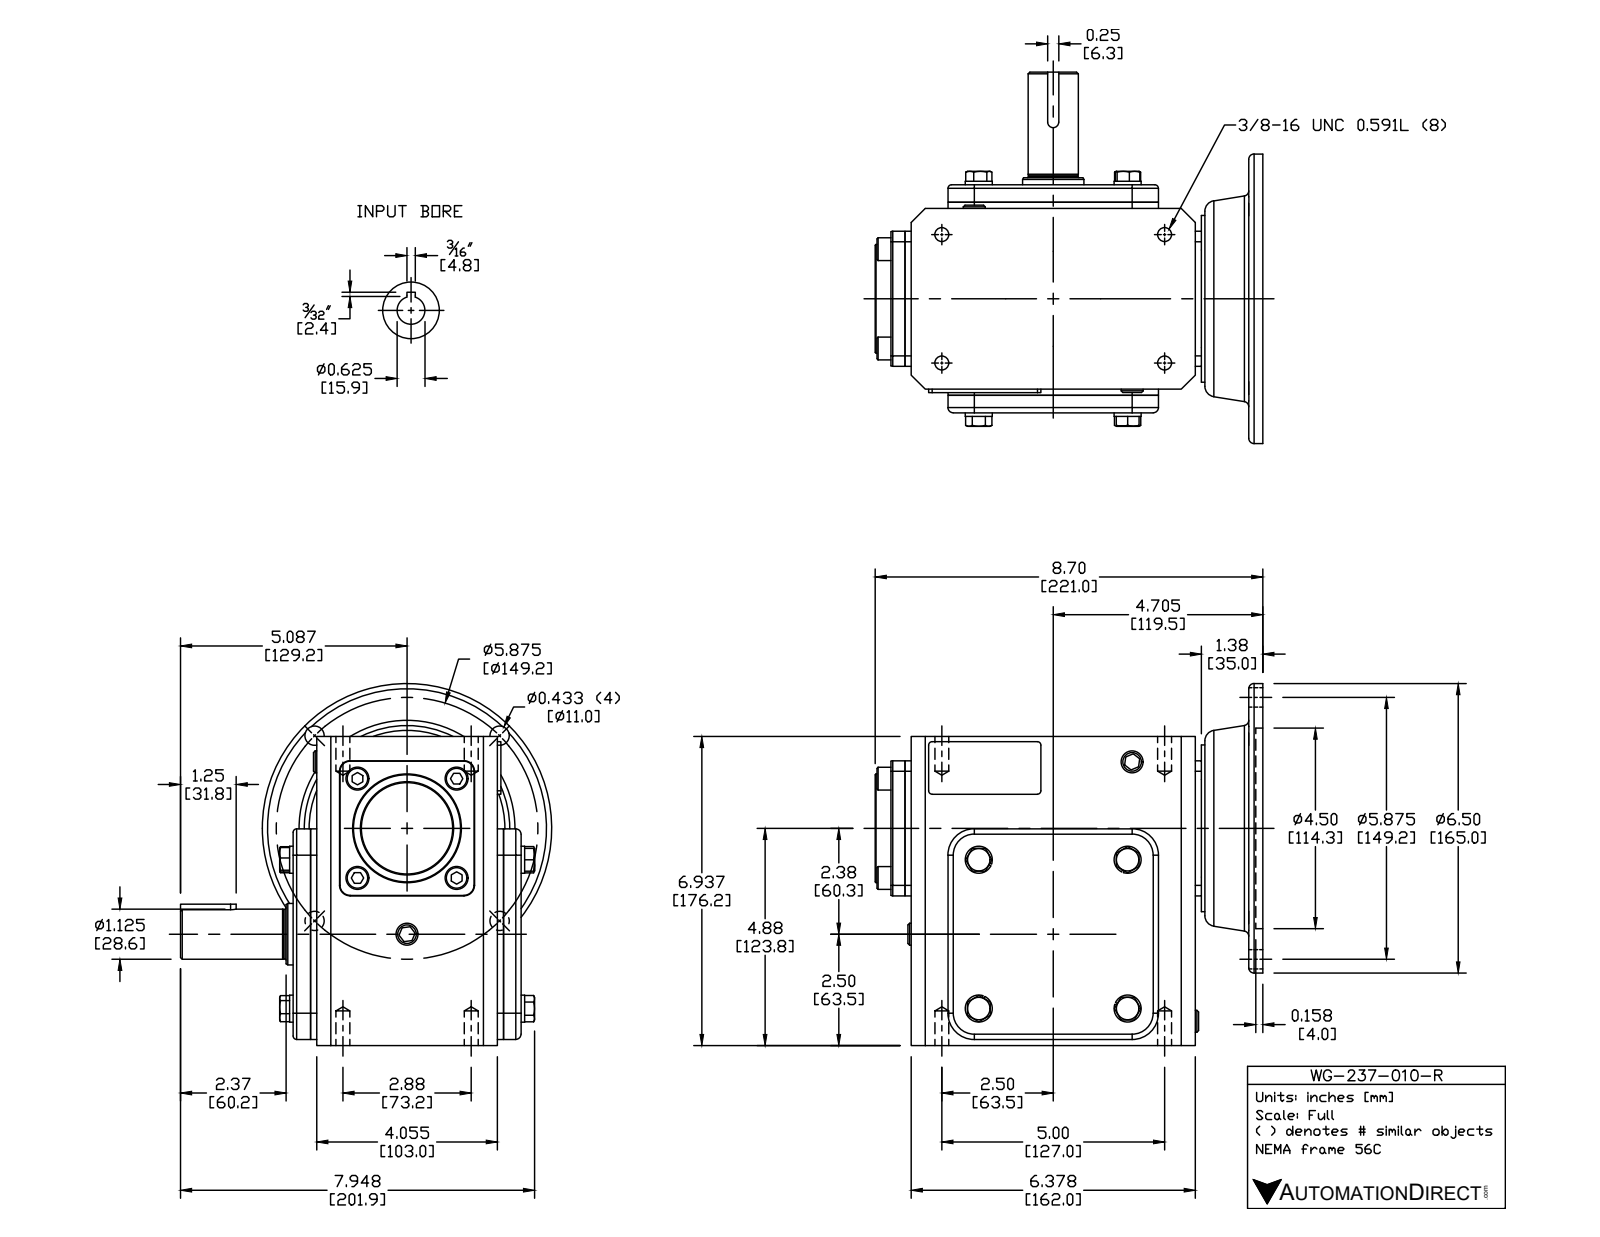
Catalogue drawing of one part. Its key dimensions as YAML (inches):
part_name: "WG-237-010-R"
step_written_by: "SolidWorks 2015 (CONFIG_CONTROL_DESIGN)"
units: inches
bodies: {solids: 37, faces: 537, planar: 294, cylindrical: 153, other: 90}
overall_size: [8.701, 8.335, 8.123]
volume: 222.4
surface_area: 508.3
round_holes:
  - {diameter: 0.313, count: 4}
  - {diameter: 0.406, count: 4}
  - {diameter: 0.591, count: 1}
  - {diameter: 0.625, count: 1}
  - {diameter: 1.378, count: 1}
  - {diameter: 1.457, count: 1}
  - {diameter: 1.772, count: 1}
  - {diameter: 3.819, count: 1}
  - {diameter: 4.5, count: 1}
round_bosses_or_shafts:
  - {diameter: 0.606, count: 4}
  - {diameter: 0.512, count: 4}
  - {diameter: 6.496, count: 1}
  - {diameter: 3.74, count: 1}
  - {diameter: 2.441, count: 1}
  - {diameter: 2.047, count: 1}
  - {diameter: 1.181, count: 1}
  - {diameter: 1.142, count: 1}
partial_cylinders:
  - {radius: 0.079, count: 12}
  - {radius: 0.236, count: 6}
  - {radius: 0.118, count: 4}
  - {radius: 0.591, count: 4}
  - {radius: 0.02, count: 2}
  - {radius: 0.039, count: 2}
  - {radius: 0.125, count: 1}
face_to_face_distances: [0.138, 4.724, 0.394, 4.331, 0.531, 4.587, 4.193, 6.516, 6.937, 0.315]
hole_center_spacings: [2.937, 2.098, 2.88, 4.154, 4.154, 4.913, 5, 5.77]
